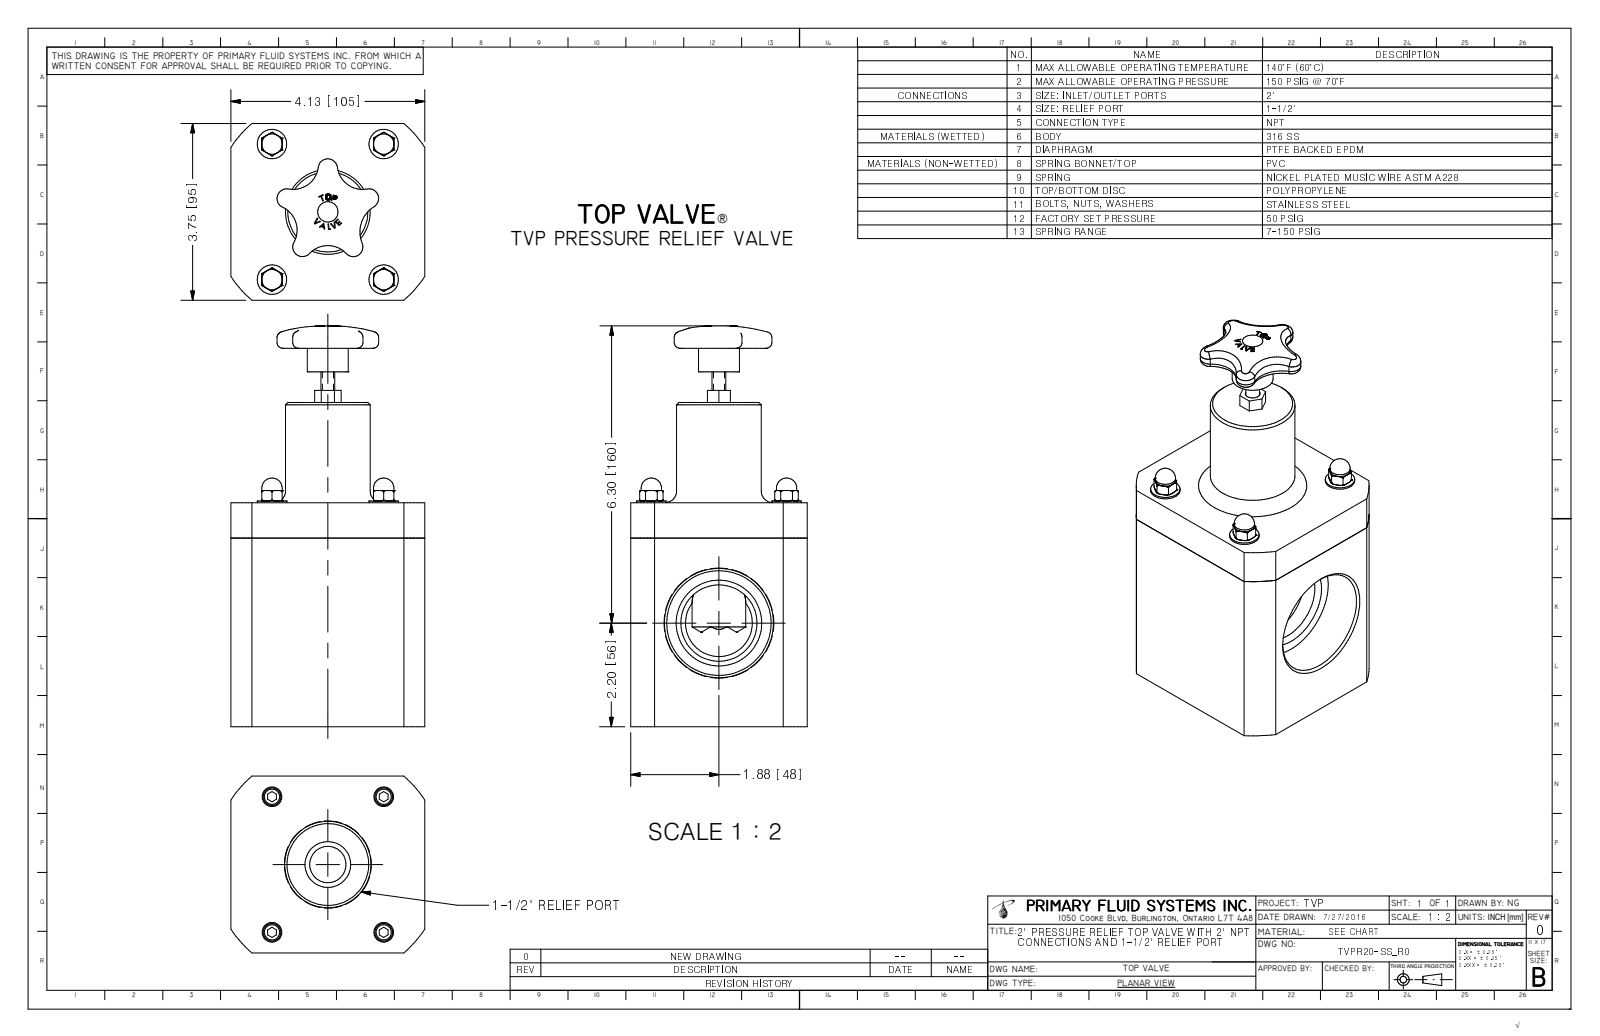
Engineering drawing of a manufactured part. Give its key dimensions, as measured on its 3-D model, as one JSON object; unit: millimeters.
{"part_name": "TVPR20-SS_R0", "step_written_by": "Autodesk Inventor 2009 (AUTOMOTIVE_DESIGN)", "units": "millimeters", "bodies": {"solids": 1, "faces": 340, "planar": 145, "cylindrical": 46, "other": 149}, "overall_size": [215.9, 104.8, 95.3], "volume_mm3": 1146000, "surface_area_mm2": 92710, "round_holes": [[4.4, 4], [44, 1], [56.4, 1]], "round_bosses_or_shafts": [[15.9, 4], [11, 4], [9.5, 4], [45.7, 1], [22.1, 1], [7.4, 1]], "partial_cylinders_radius": [[2.2, 5], [5.2, 5], [13.6, 4], [16.7, 4], [15.9, 1], [18.9, 1], [62.9, 1]], "face_to_face_distances": [95.3, 120.7, 104.8, 22.9, 81.9, 59.1, 15.2, 105.4, 174.6, 159.4], "hole_center_spacings": [47.3, 47.4, 60.3, 73, 94.7]}
